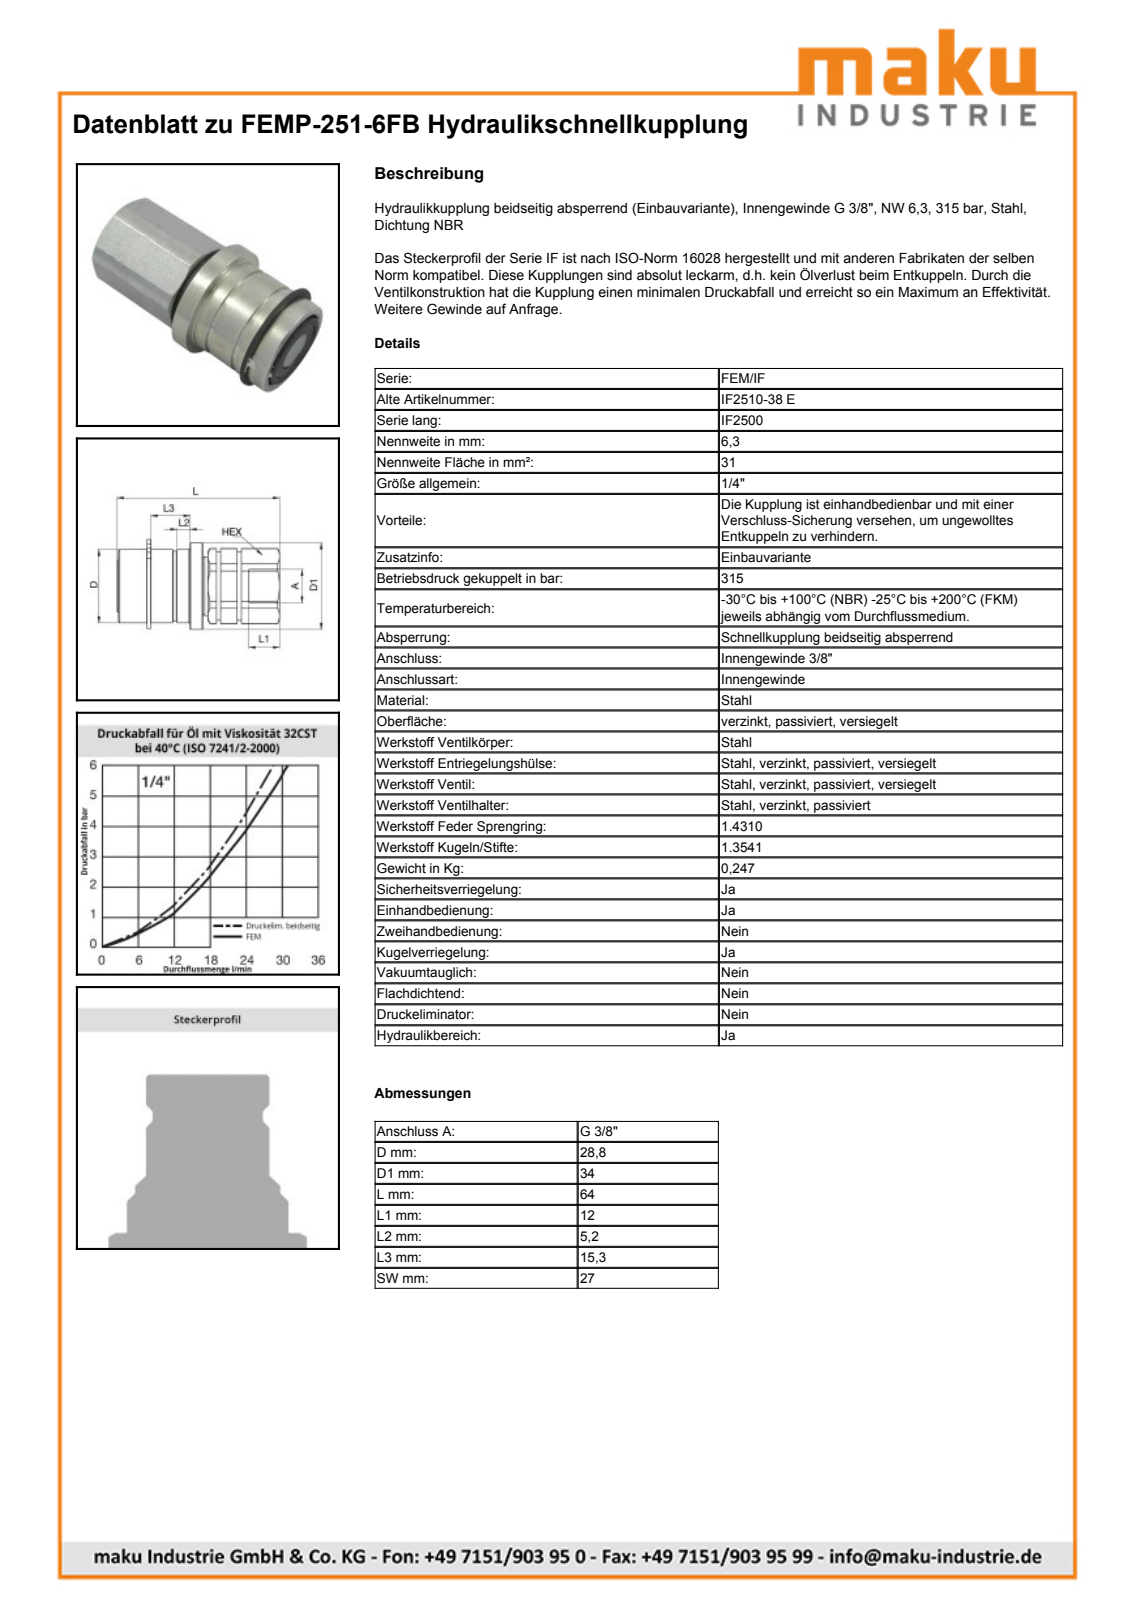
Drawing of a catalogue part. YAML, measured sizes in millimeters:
part_name: "FEMP-251-6FB"
step_written_by: "SolidWorks 2009 (AUTOMOTIVE_DESIGN)"
units: millimeters
bodies: {solids: 2, faces: 152, planar: 32, cylindrical: 59, other: 61}
overall_size: [63.6, 35.25, 34]
volume: 38597
surface_area: 10251
round_holes:
  - {diameter: 2.4, count: 2}
  - {diameter: 9.65, count: 1}
  - {diameter: 14.95, count: 1}
  - {diameter: 16.2, count: 1}
  - {diameter: 20.92, count: 1}
  - {diameter: 21.5, count: 1}
  - {diameter: 22.2, count: 1}
  - {diameter: 24.2, count: 1}
  - {diameter: 25.1, count: 1}
round_bosses_or_shafts:
  - {diameter: 34, count: 1}
  - {diameter: 28.8, count: 1}
  - {diameter: 27.5, count: 1}
  - {diameter: 23, count: 1}
  - {diameter: 22.1, count: 1}
  - {diameter: 20.7, count: 1}
  - {diameter: 20.4, count: 1}
  - {diameter: 16.1, count: 1}
partial_cylinders:
  - {radius: 2.5, count: 2}
  - {radius: 7, count: 2}
  - {radius: 14.75, count: 1}
  - {radius: 16.12, count: 1}
  - {radius: 18.32, count: 1}
face_to_face_distances: [27, 30.1, 26.99, 63.1, 33, 50.6, 20.5, 12.5, 52, 21.9]
hole_center_spacings: [15.74, 9.6]
